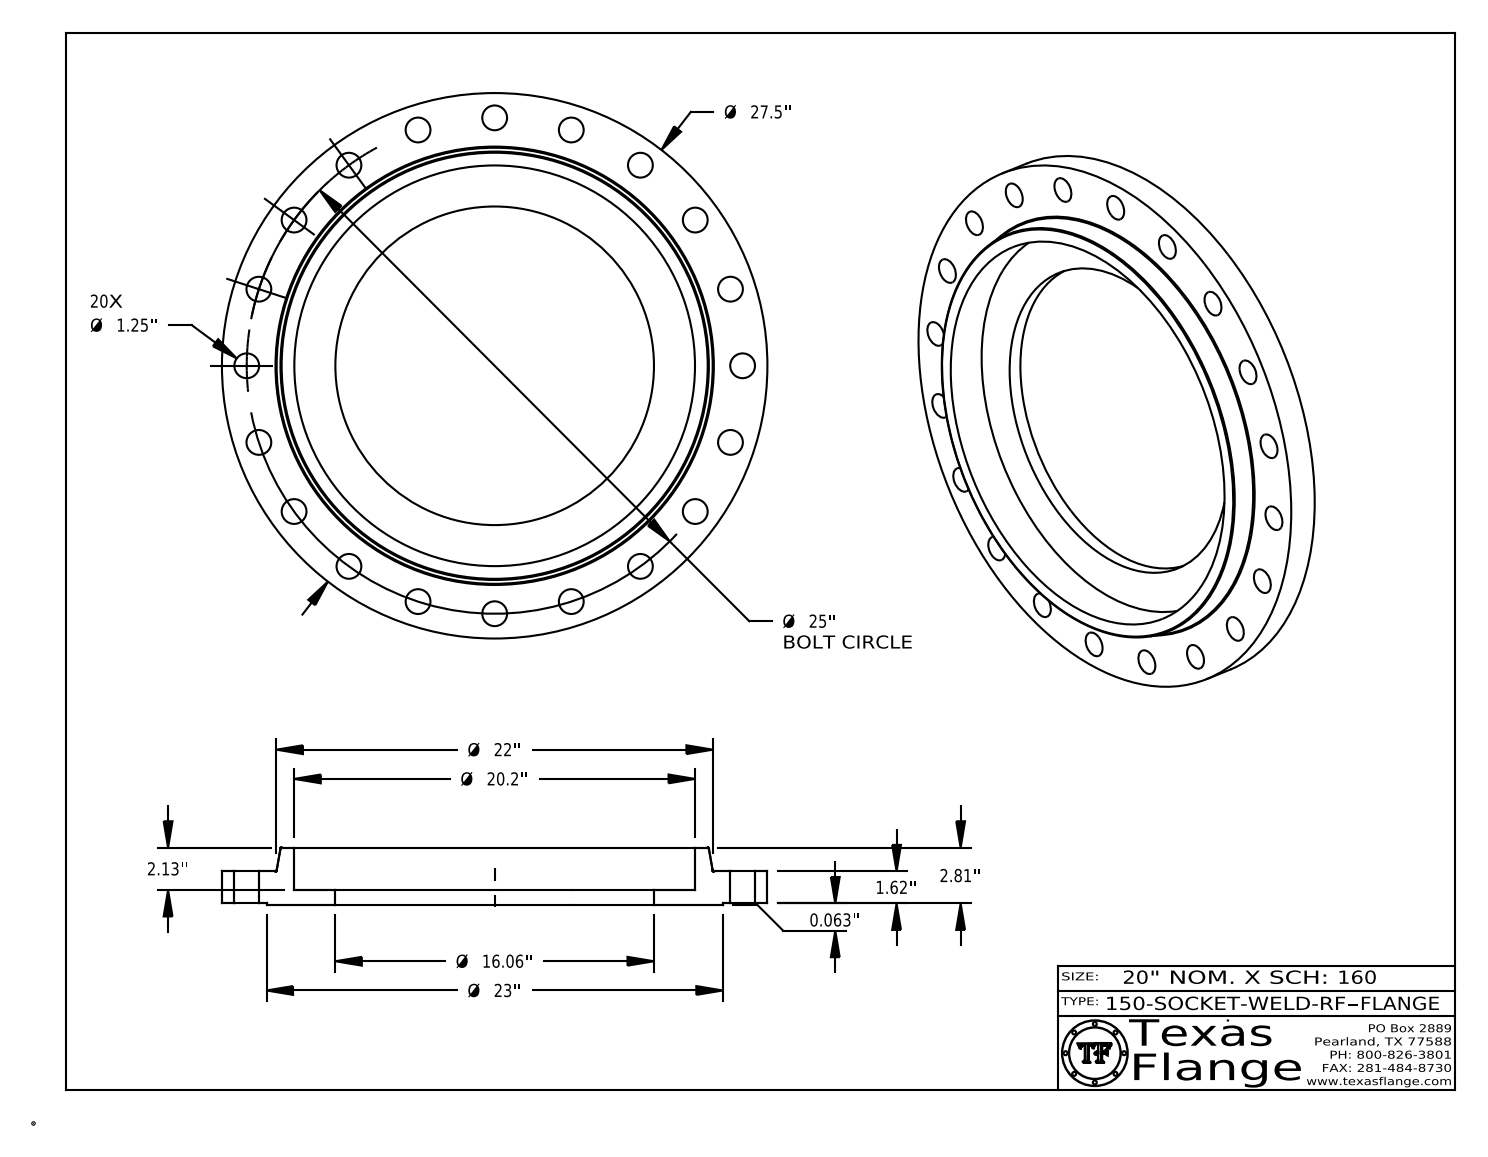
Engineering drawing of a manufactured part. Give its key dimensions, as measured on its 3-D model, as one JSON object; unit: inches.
{"part_name": "150-SOCKET-WELD-RF", "step_written_by": "CATIA V5 STEP AP214 (AUTOMOTIVE_DESIGN)", "units": "inches", "bodies": {"solids": 1, "faces": 444, "planar": 370, "cylindrical": 68, "other": 6}, "overall_size": [27.5, 27.5, 2.873], "volume_in3": 559.1, "surface_area_in2": 1244, "round_holes": [[1.25, 20], [0.495, 1], [16.062, 1], [20.2, 1]], "round_bosses_or_shafts": [[0.03, 8], [27.5, 1], [23, 1], [0.39, 1]], "face_to_face_distances": [1.683, 0.063, 1.62, 0.743, 0.68, 0.94, 2.872, 2.81, 2.13, 1.19], "hole_center_spacings": [12.5, 14.694, 17.678, 20.225, 23.776, 24.692, 11.35, 22.275]}
